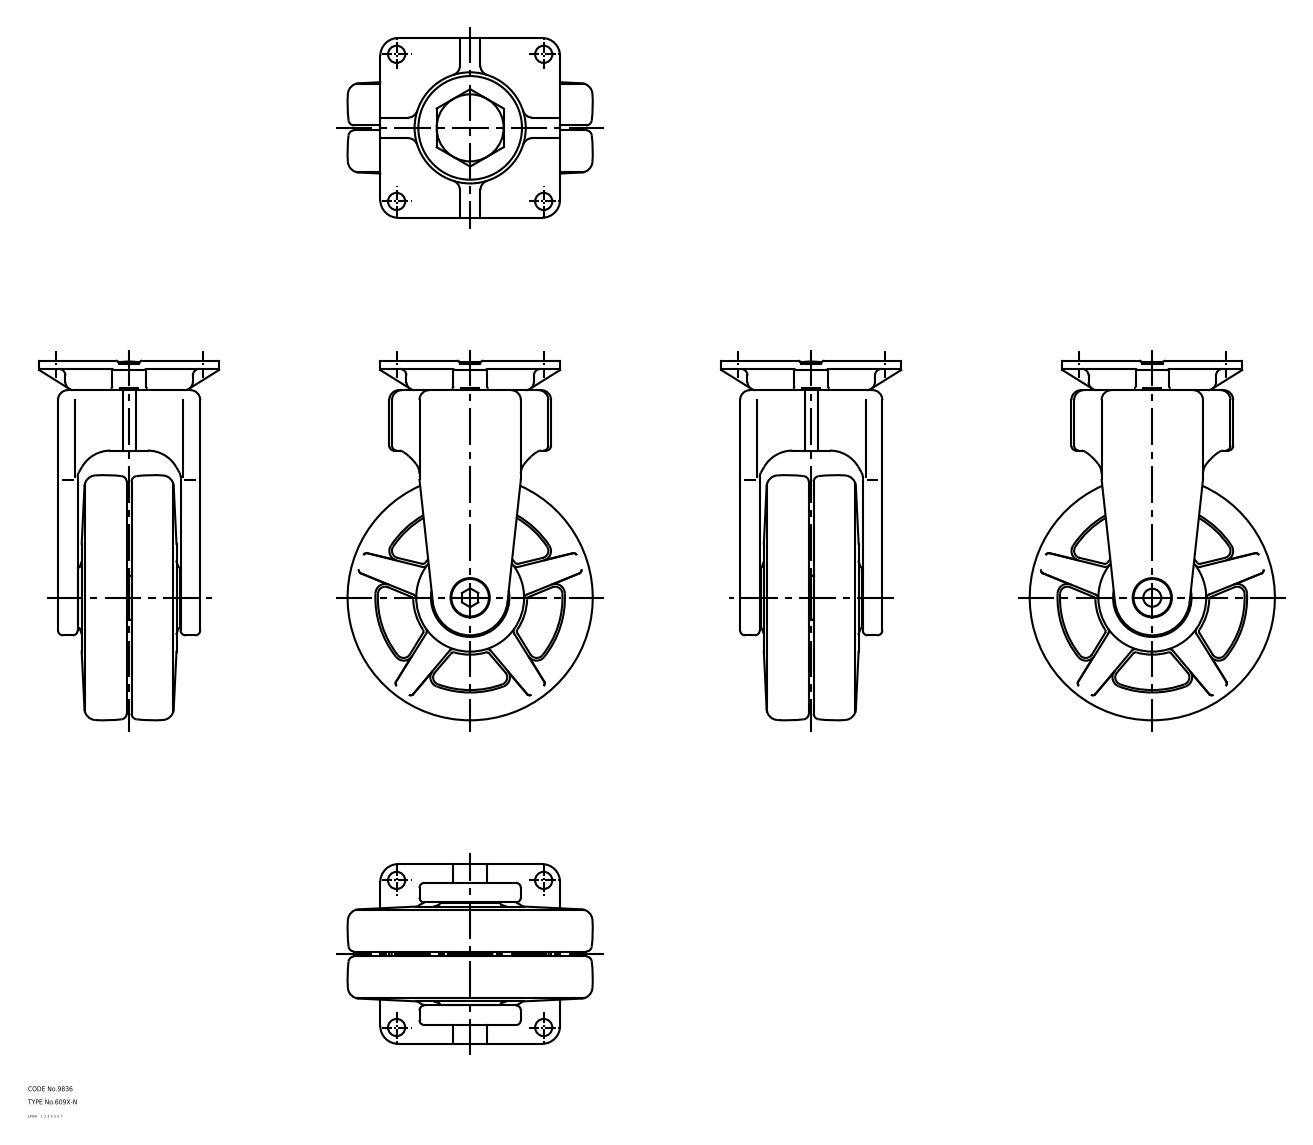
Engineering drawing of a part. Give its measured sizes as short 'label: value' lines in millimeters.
name: 67172756; 67172769; 67172782; 67172795 (+8 more)
written by: CADfix (AUTOMOTIVE_DESIGN)
unit: mm
bodies: 4 solids, 718 faces (0 planar, 0 cylindrical, 718 other)
size: 220 × 150 × 110
volume: 397 522 mm³; area: 199 285 mm²
